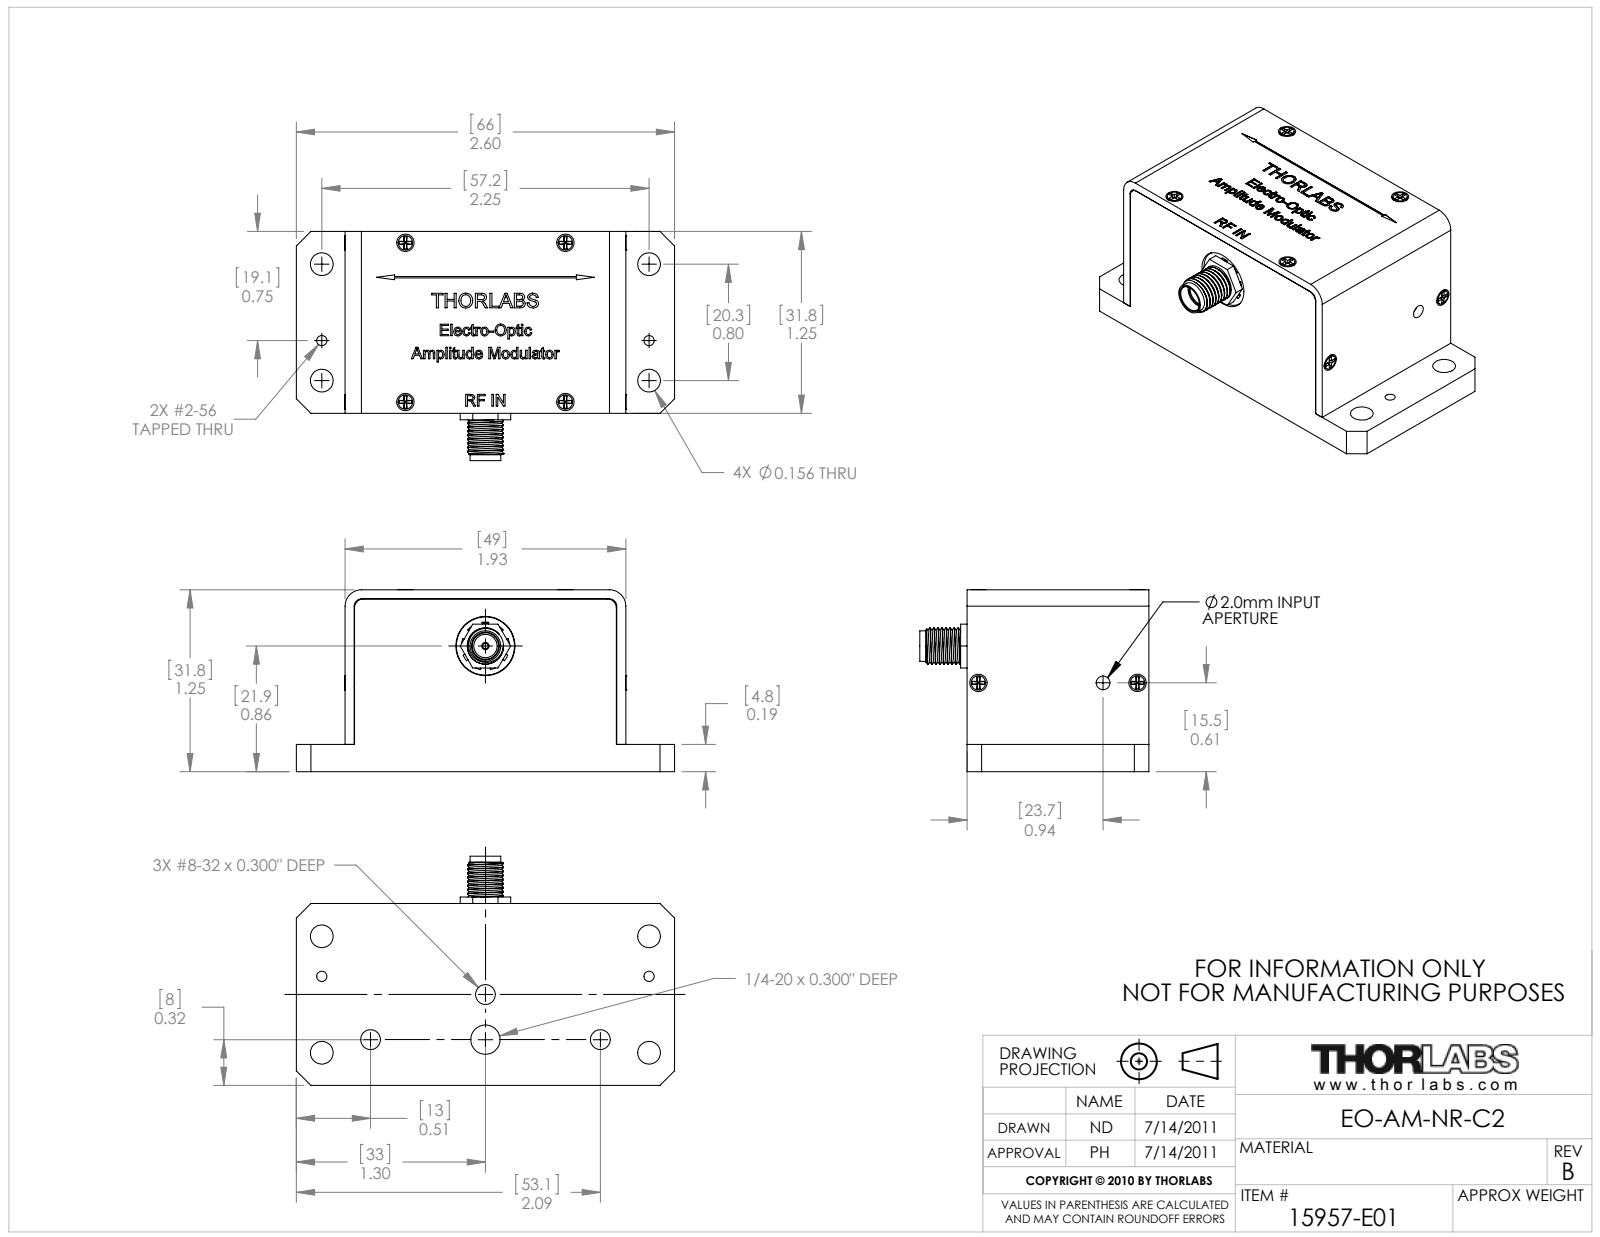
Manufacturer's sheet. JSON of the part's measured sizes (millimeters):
{"part_name": "15957-E01", "step_written_by": "SolidWorks 2011 (AUTOMOTIVE_DESIGN)", "units": "millimeters", "bodies": {"solids": 13, "faces": 1048, "planar": 588, "cylindrical": 172, "other": 288}, "overall_size": [66.04, 40.01, 31.79], "volume_mm3": 28212, "surface_area_mm2": 18817, "round_holes": [[1.78, 8], [1.19, 6], [3.96, 4], [3.45, 3], [0.94, 1], [1.27, 1], [2.38, 1], [4.06, 1], [4.19, 1], [4.6, 1], [5.11, 1], [6.35, 1]], "round_bosses_or_shafts": [[2.51, 6], [1.52, 6], [10.16, 1], [8, 1], [6.3, 1], [5.33, 1], [1.27, 1]], "partial_cylinders_radius": [[1.59, 5], [1.27, 2], [2.86, 2], [3.26, 2], [3.49, 1], [4.19, 1]], "face_to_face_distances": [31.76, 3.18, 28.58, 30.18, 1.59, 47.43, 25.4, 1.58, 8.89, 21.29], "hole_center_spacings": [15.08, 19.7, 28.14, 30.33, 42.71, 48.88, 27.78, 57.16]}
